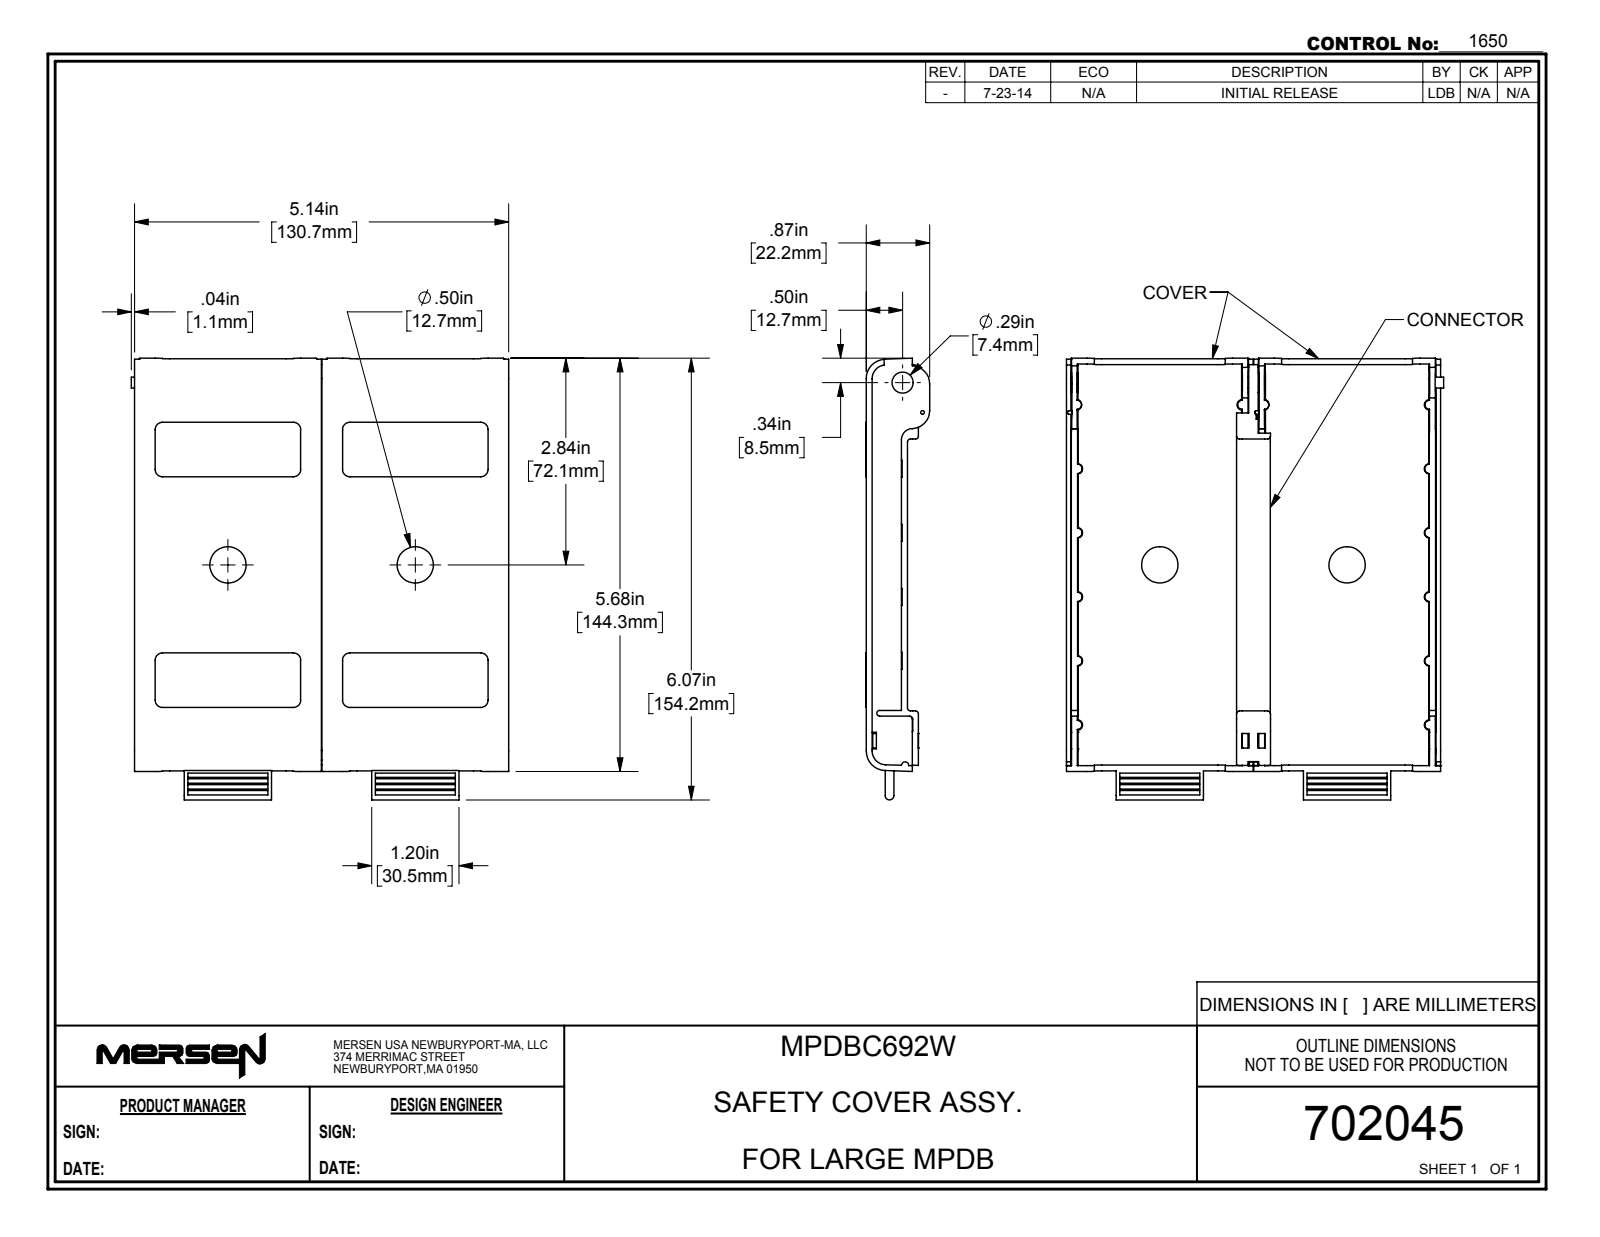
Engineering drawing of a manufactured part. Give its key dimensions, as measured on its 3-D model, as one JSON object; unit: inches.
{"part_name": "702045", "step_written_by": "SolidWorks 2017 (AUTOMOTIVE_DESIGN)", "units": "inches", "bodies": {"solids": 0, "faces": 348, "planar": 207, "cylindrical": 107, "other": 34}, "overall_size": [6.071, 5.188, 0.874], "round_holes": [[0.5, 2], [0.157, 1], [0.29, 1]], "round_bosses_or_shafts": [[0.268, 1], [0.15, 1], [0.05, 1]], "partial_cylinders_radius": [[0.1, 18], [0.039, 9], [0.03, 8], [0.25, 6], [0.04, 5], [0.079, 4], [0.19, 2], [0.197, 2]], "face_to_face_distances": [0.08, 2.576, 2.347, 0.081, 2.566, 0.229, 0.219, 2.356, 4.922, 2.735], "hole_center_spacings": [2.576]}
